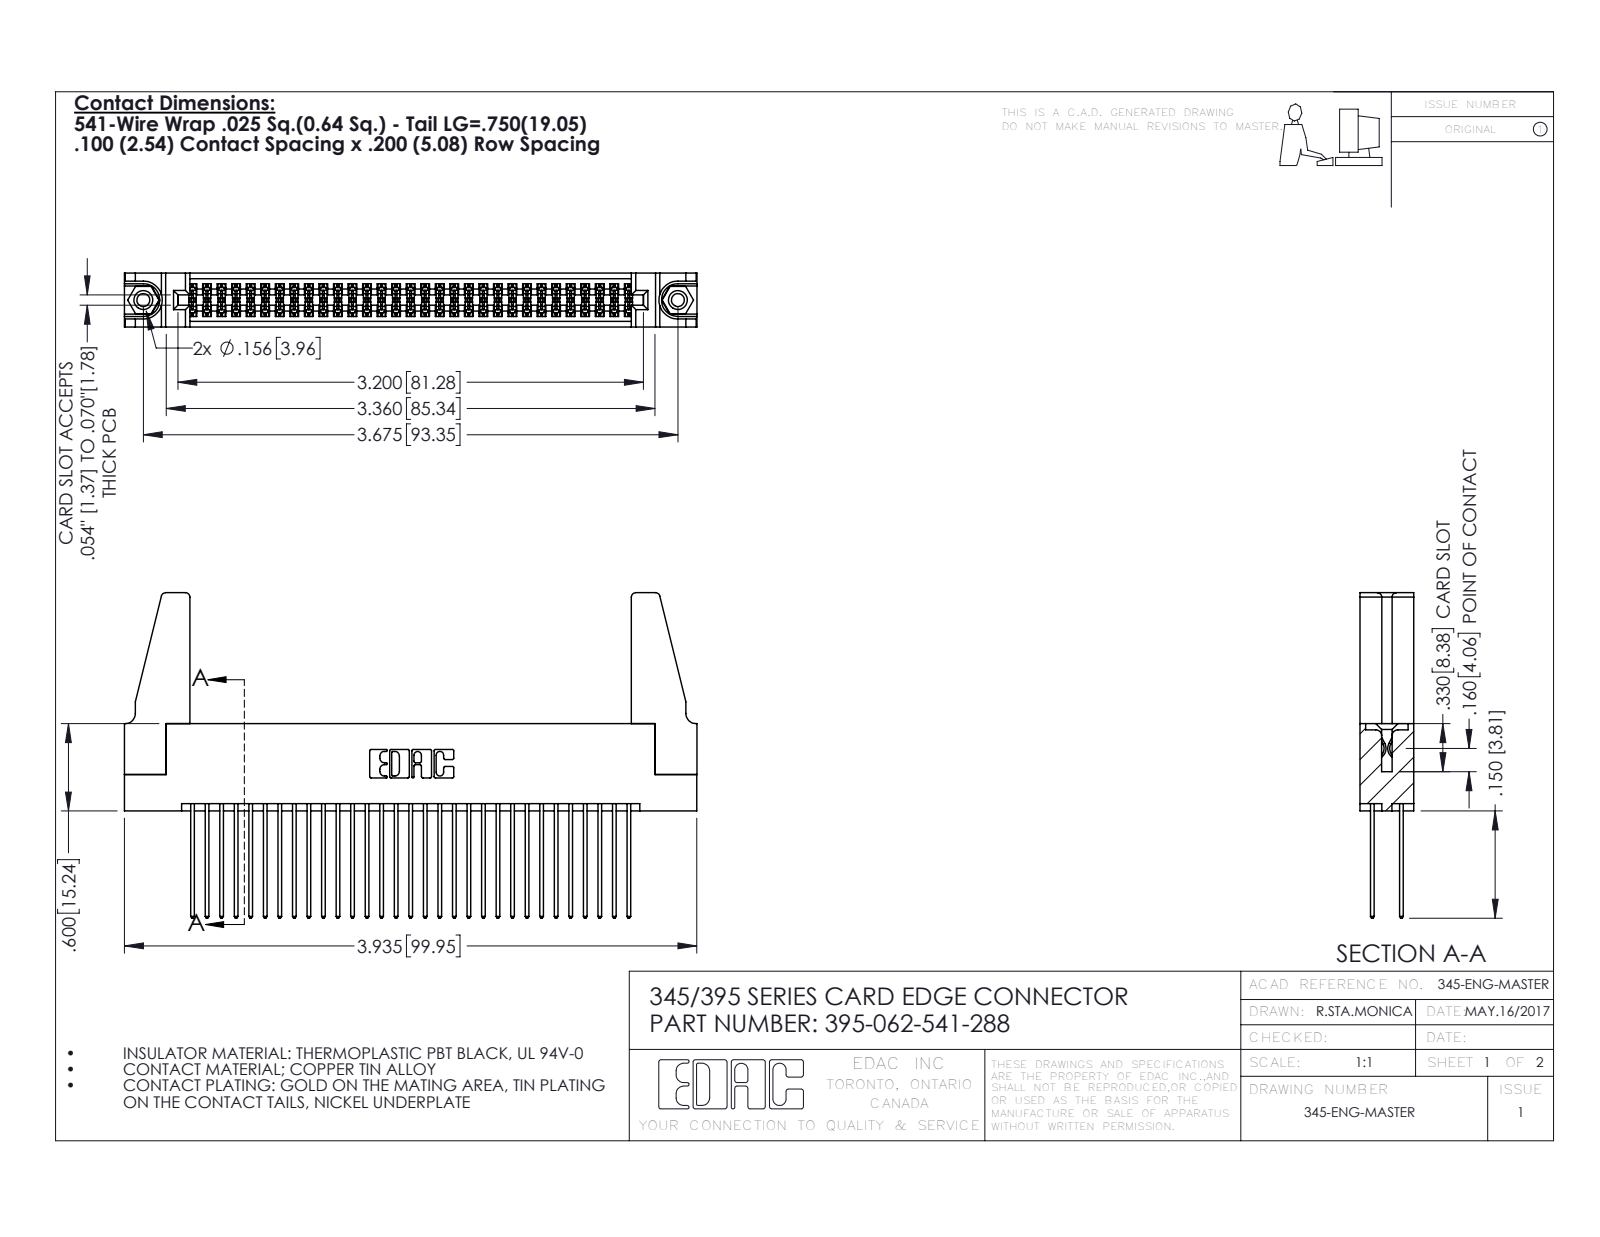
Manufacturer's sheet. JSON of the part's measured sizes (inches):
{"part_name": "345 Part_Flush Mounting Lugs - 0.156 Dia-TH; 395-062-541-288; 345-220-078_345-220-088; 345-250-001_345-250-001-102 (+1 more)", "step_written_by": "SolidWorks 2016 (CONFIG_CONTROL_DESIGN)", "units": "inches", "bodies": {"solids": 67, "faces": 3350, "planar": 2198, "cylindrical": 1136, "other": 16}, "overall_size": [3.936, 2.237, 0.37], "volume_in3": 0.807, "surface_area_in2": 29.93, "round_holes": [[0.089, 2], [0.125, 2], [0.156, 2], [0.064, 1]], "round_bosses_or_shafts": [[0.155, 2]], "partial_cylinders_radius": [[0.006, 93], [0.01, 62], [0.01, 22], [0.03, 8], [0.007, 6], [0.031, 6], [0.026, 3], [0.014, 2]], "face_to_face_distances": [0.072, 0.298, 0.2, 0.098, 0.272, 0.025, 0.37, 0.225, 0.175, 0.149], "hole_center_spacings": [0.27, 3.44, 3.675]}
